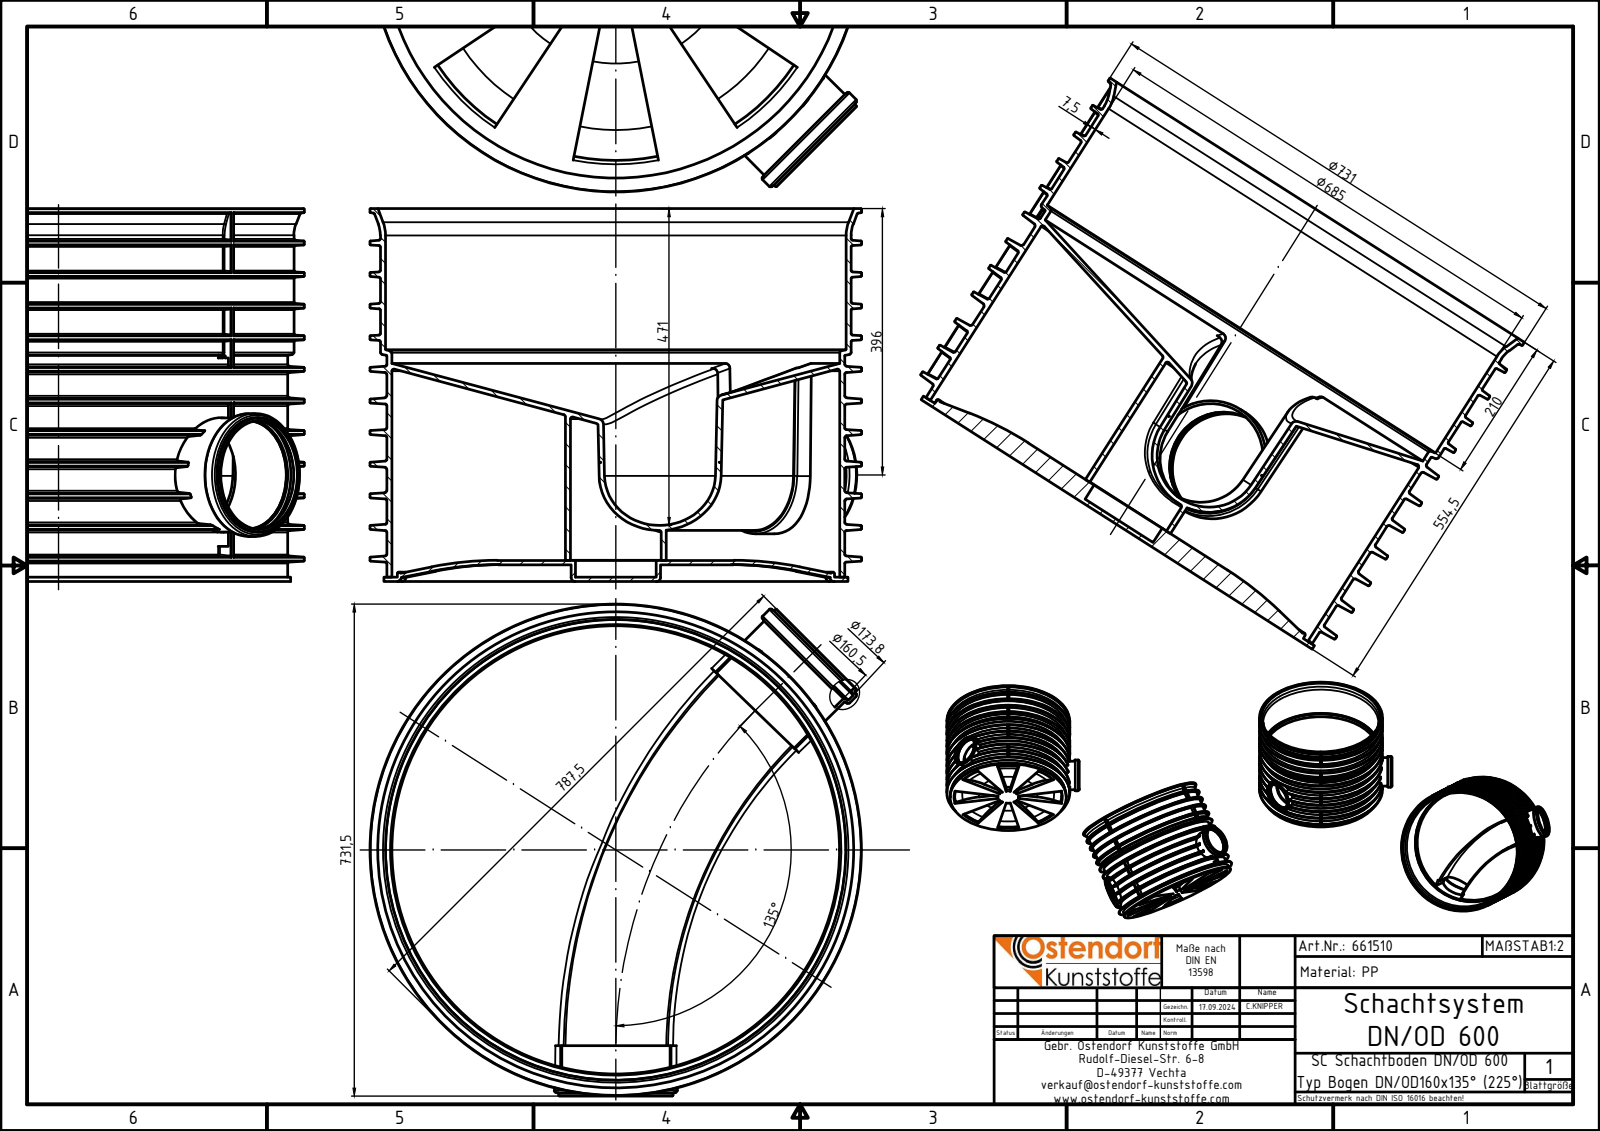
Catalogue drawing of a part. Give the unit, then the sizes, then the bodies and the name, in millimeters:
Units: millimetres
Overall size (bounding box): 731.5 × 731 × 554.5
Round holes (diameter × count): ⌀160.5 ×2, ⌀160.7 ×2, ⌀160.8 ×2, ⌀173.8 ×2, ⌀120 ×1, ⌀135 ×1, ⌀169.8 ×1, ⌀640 ×1, ⌀666 ×1, ⌀685 ×1
Round bosses / shafts (diameter × count): ⌀182.8 ×2, ⌀731 ×1, ⌀700 ×1, ⌀690 ×1, ⌀681 ×1, ⌀650 ×1, ⌀169.8 ×1, ⌀169.5 ×1
Partial cylindrical surfaces — rounded edges, fillets, slot ends (radius × count): R2 ×16, R1 ×10, R2.5 ×2, R3 ×2, R82.5 ×2, R87.5 ×2, R66.5 ×1, R84.75 ×1
Main face-to-face distances: 6.5, 25, 31.5, 18.5, 554.5, 548, 529.5, 523, 7.5, 11
Volume: 23 170 000 mm³ · Surface area: 5 477 000 mm²
Bodies: 2 solids, 1539 faces (154 planar, 275 cylindrical, 1110 other)
Part name (STEP PRODUCT): 661510z; 661510 Schacht DN600 Boden; 661510 Schachtboden DN600 Grundkörper
STEP written by: Autodesk Inventor 2024 (AUTOMOTIVE_DESIGN)
